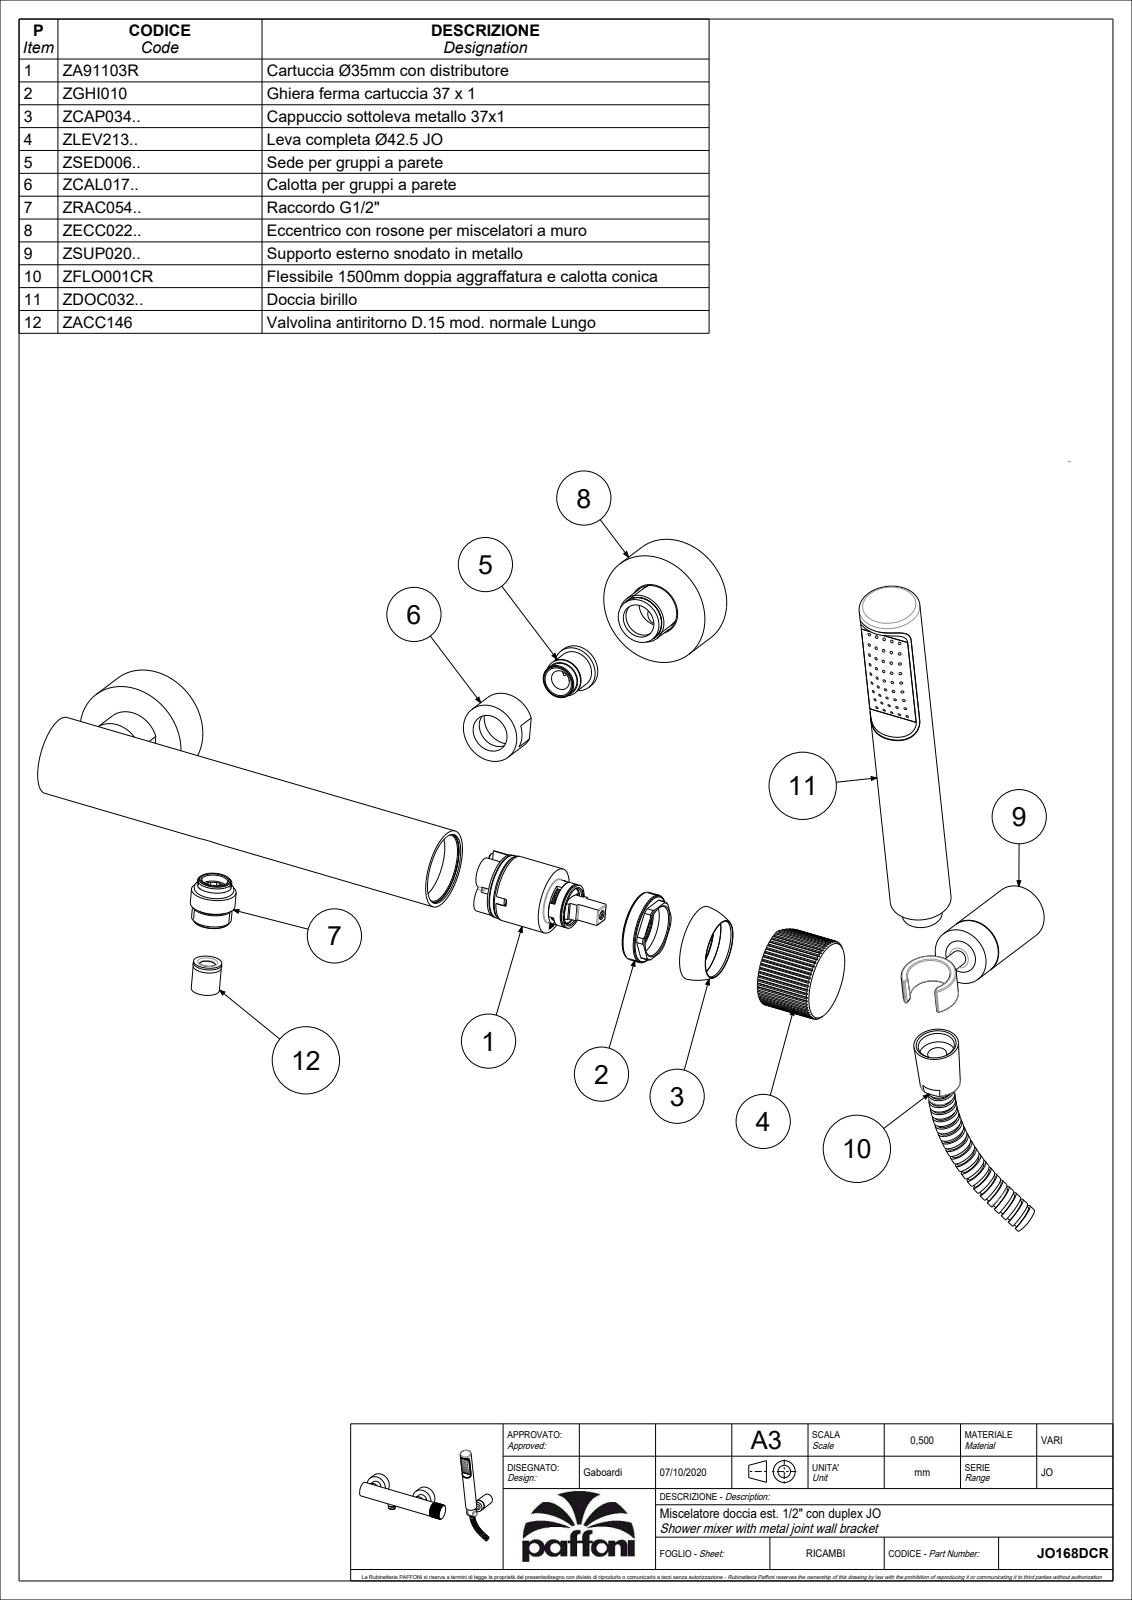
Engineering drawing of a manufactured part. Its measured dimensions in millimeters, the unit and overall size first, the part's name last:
Units: millimetres
Overall size (bounding box): 427.94 × 316.37 × 192.55
Round holes (diameter × count): ⌀1.5 ×45, ⌀7.5 ×6, ⌀8 ×3, ⌀9 ×3, ⌀12 ×3, ⌀16.7 ×3, ⌀4 ×2, ⌀10.5 ×2, ⌀18 ×2, ⌀20 ×2, ⌀24.5 ×2, ⌀25.5 ×2
Round bosses / shafts (diameter × count): ⌀59.7 ×2, ⌀31.5 ×2, ⌀24 ×2, ⌀23.5 ×2, ⌀19.7 ×2, ⌀41.5 ×1, ⌀35 ×1, ⌀34.8 ×1
Partial cylindrical surfaces — rounded edges, fillets, slot ends (radius × count): R0.5 ×54, R0.15 ×11, R0.3 ×9, R1 ×4, R7 ×4, R4.5 ×2, R7.8 ×2, R7.95 ×2
Main face-to-face distances: 5, 25, 20, 10, 23, 18, 43, 3, 2, 23.5
Hole centre spacings: 7.91, 20.01, 6.5, 13, 26.38, 13.76, 4.5, 11.1
Volume: 468 454 mm³ · Surface area: 182 439 mm²
Bodies: 3 solids, 1344 faces (633 planar, 445 cylindrical, 266 other)
Part name (STEP PRODUCT): JO168DCR
STEP written by: CREO PARAMETRIC BY PTC INC, 2020044 (CONFIG_CONTROL_DESIGN)
